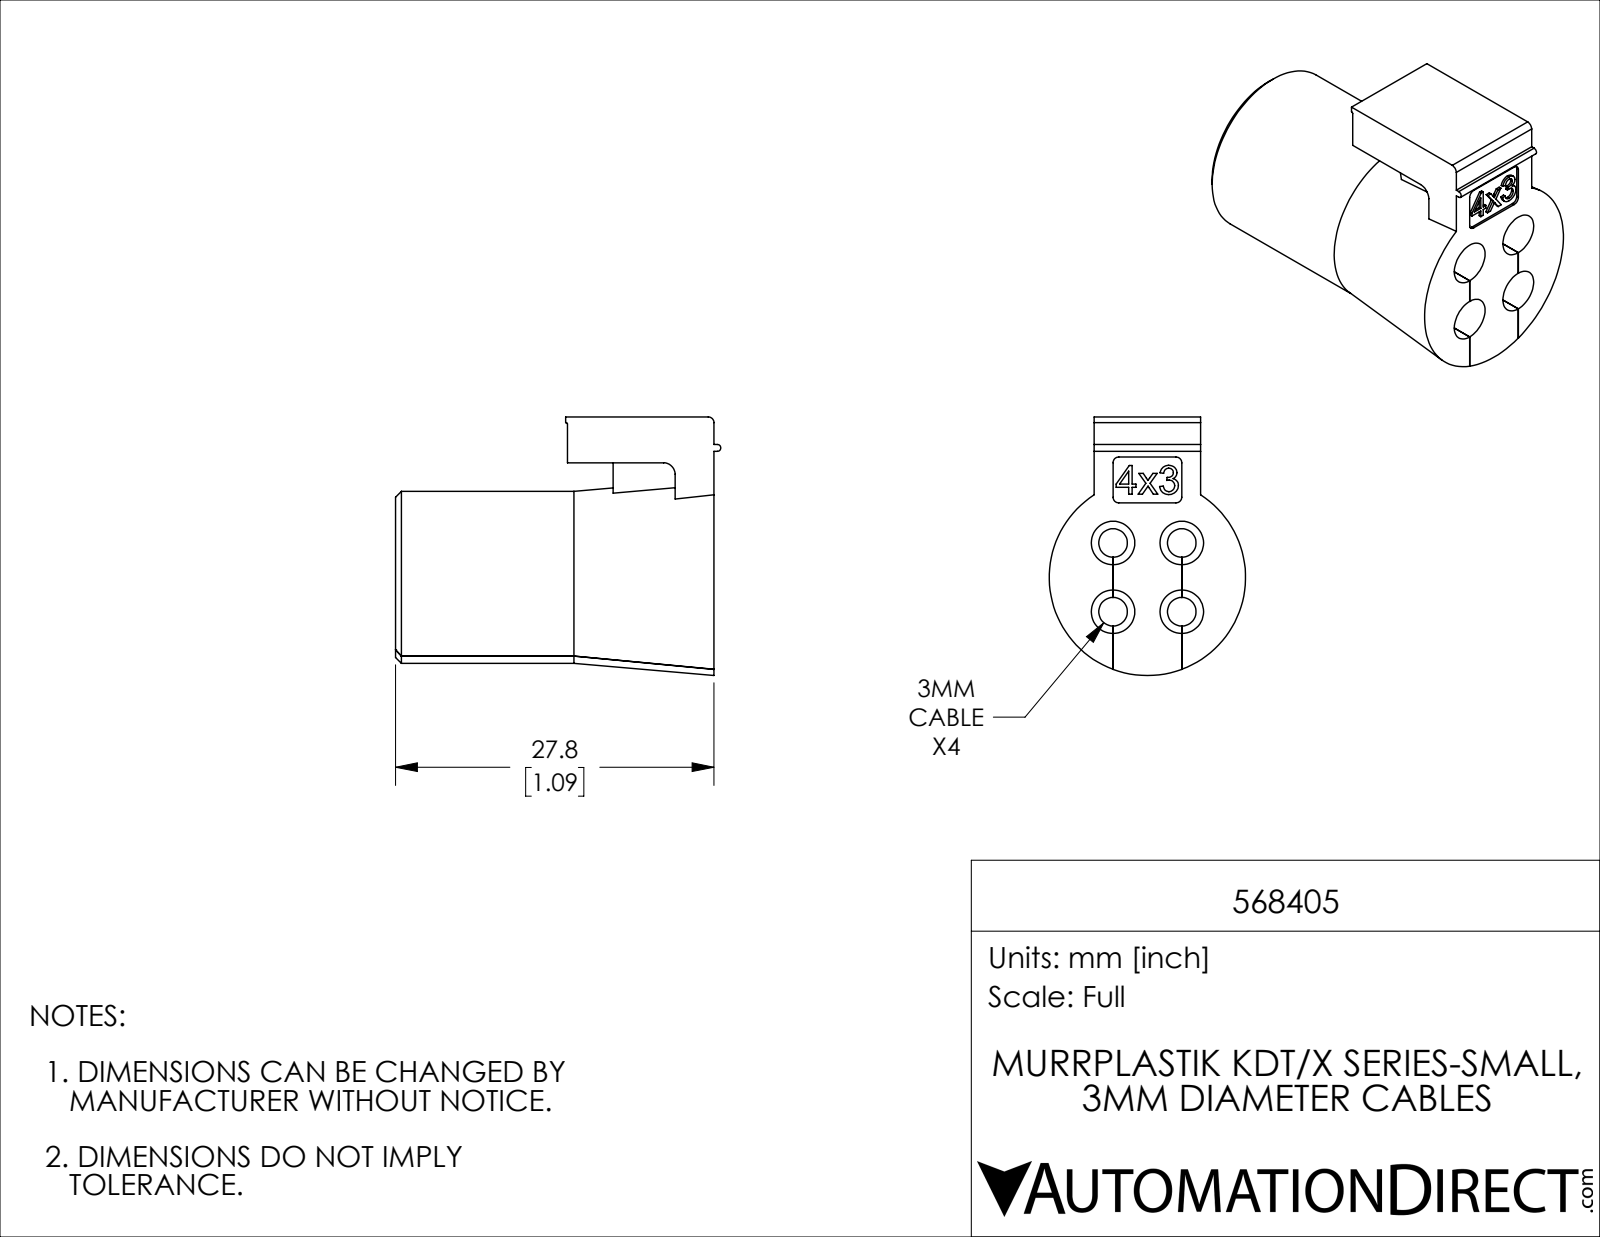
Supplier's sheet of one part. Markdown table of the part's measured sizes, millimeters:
| quantity | value |
| --- | --- |
| part name | 568405 |
| STEP written by | SolidWorks 2019 (CONFIG_CONTROL_DESIGN) |
| units | millimeters |
| bodies | 1 solid, 144 faces (64 planar, 40 cylindrical, 40 other) |
| overall size | 28.4 × 22.6 × 17.1 |
| volume | 4 590 mm³ |
| surface area | 3 890 mm² |
| round holes (diameter × count) | 2.5 × 4, 3.8 × 4 |
| round bosses / shafts (diameter × count) | 15 × 1 |
| partial cylindrical surfaces (radius × count) | 0.5 × 5, 0.1 × 1, 0.3 × 1, 1 × 1 |
| main face-to-face distances | 6, 6, 6, 1.7, 1.7, 7.6, 7.7, 27.8, 4, 9.3 |
| hole center spacings | 6, 8.5 |
